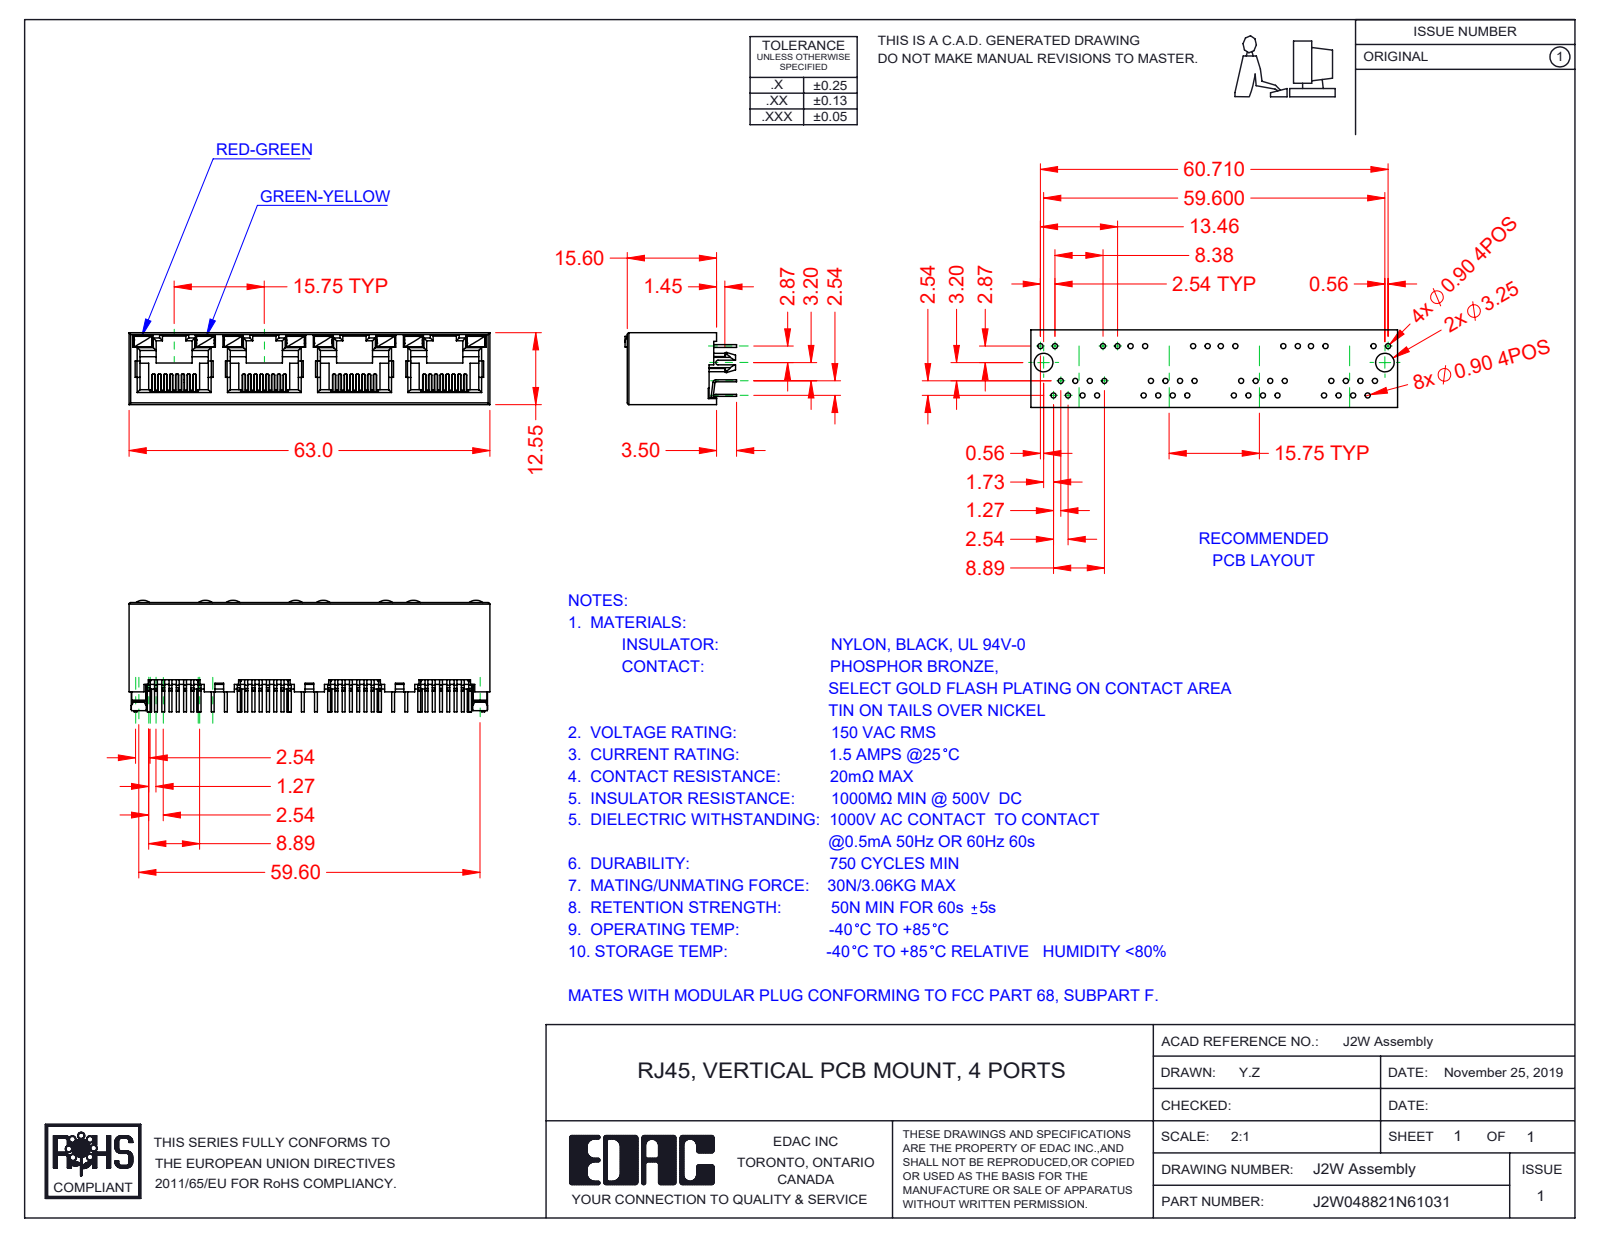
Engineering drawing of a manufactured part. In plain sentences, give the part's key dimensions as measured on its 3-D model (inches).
The part is named "J2W048821N65131; 2W LED RH_5-Green-Yellow; 2W LED LH_6-Red-Green; 2W Contact Lock (+2 more)". Its 3-D file was written by "SolidWorks 2016 (CONFIG_CONTROL_DESIGN)". It is 45 solids with 3143 faces: 2600 planar, 485 cylindrical and 58 other. Overall it measures 2.48 by 0.768 by 0.494 inches. Its volume is 0.326 cubic inches and its surface area 20.37 square inches. Partial cylindrical surfaces (rounded edges, fillets, slot ends): 64 of radius 0.006, 29 of radius 0.008, 28 of radius 0.02, 14 of radius 0.012, 8 of radius 0.018, 8 of radius 0.079, 2 of radius 0.01, 2 of radius 0.059. The main face-to-face distances are 0.494, 0.469, 0.026, 0.62, 0.014, 0.059, 0.031, 0.024, 0.445, 1.24.
